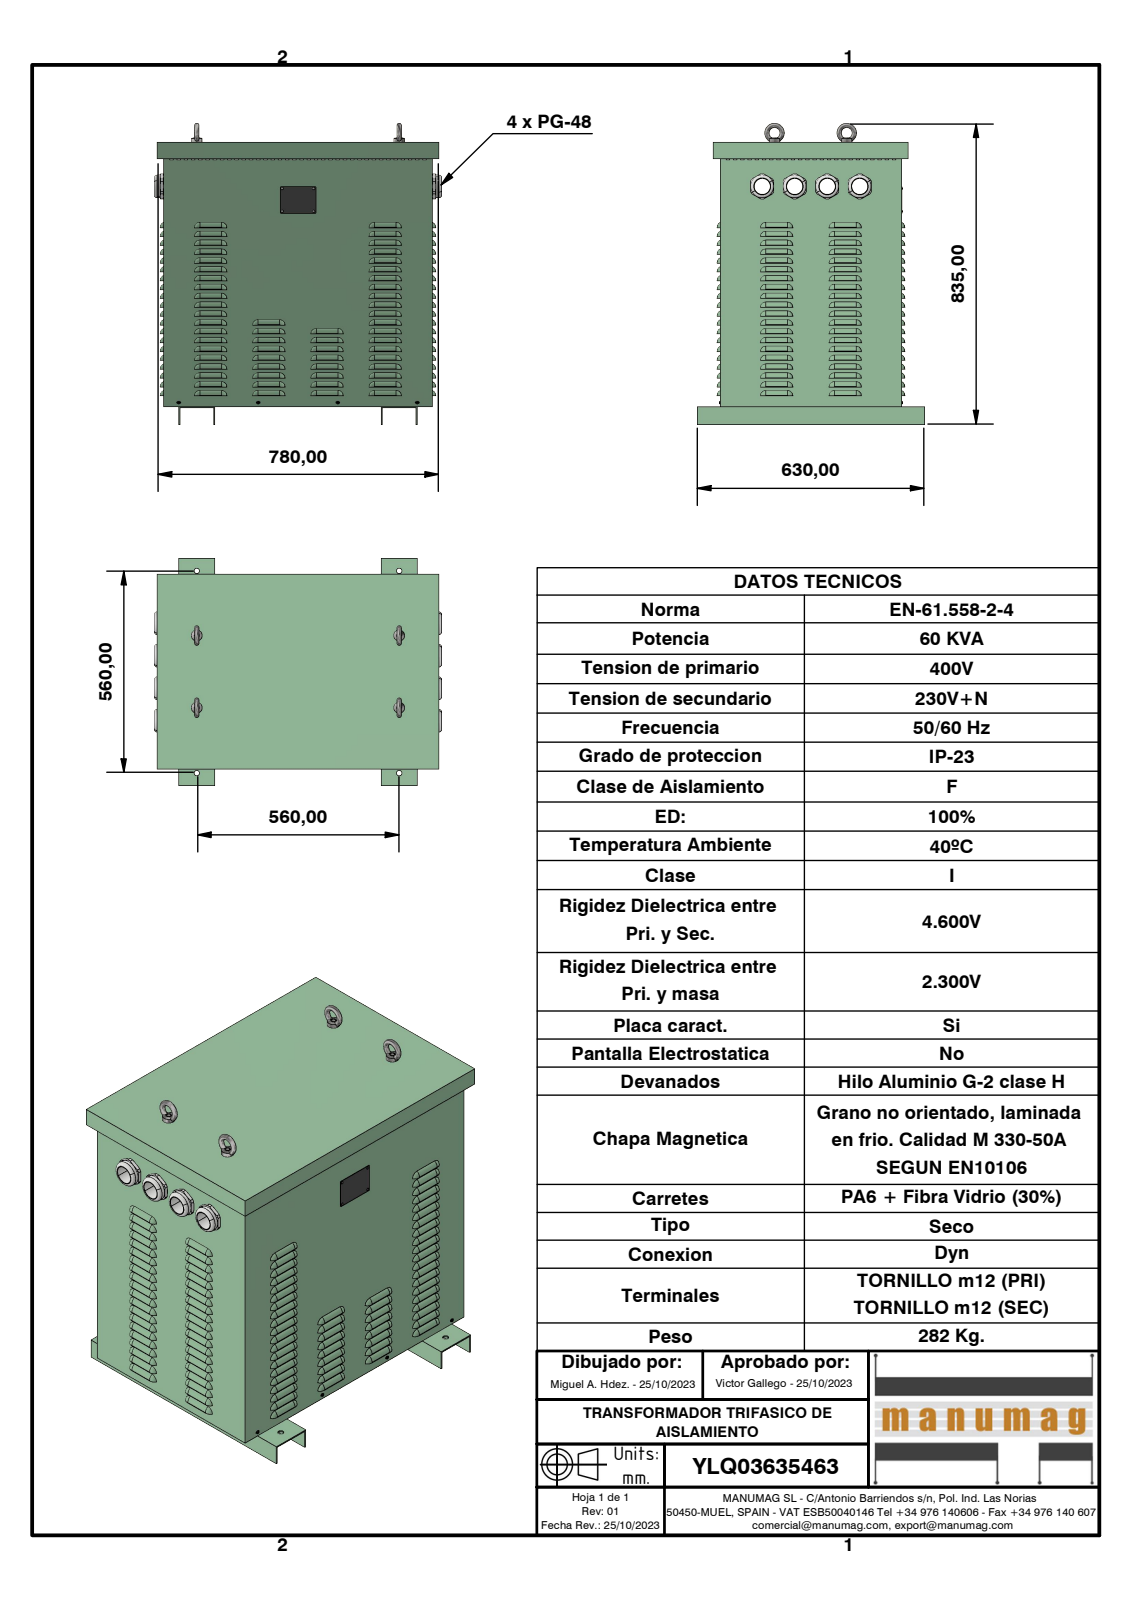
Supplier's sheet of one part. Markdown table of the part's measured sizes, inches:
| quantity | value |
| --- | --- |
| part name | YLQ03635463; JE200 CUERPO; JE160 EXPORT JE200 EXPORT NACIONAL BASE; JE160 EXPORT JE200 EXPORT NACIONAL PATA (+6 more) |
| STEP written by | Autodesk Inventor 2023 (AUTOMOTIVE_DESIGN) |
| units | inches |
| bodies | 30 solids, 4663 faces (1571 planar, 1992 cylindrical, 1100 other) |
| overall size | 32.874 × 31.31 × 24.803 |
| volume | 463 in³ |
| surface area | 9 880 in² |
| round holes (diameter × count) | 0.433 × 936, 0.591 × 12, 0.157 × 4, 0.197 × 4, 0.398 × 4, 1.732 × 4, 2.362 × 4 |
| round bosses / shafts (diameter × count) | 2.48 × 4, 2.335 × 4, 2.329 × 4, 2.269 × 4, 1.181 × 4, 0.157 × 4, 0.143 × 4, 0.126 × 4 |
| partial cylindrical surfaces (radius × count) | 0.551 × 194, 0.276 × 80, 0.591 × 80, 0.098 × 8, 0.079 × 4, 1.378 × 4 |
| main face-to-face distances | 0.079, 19.685, 28.74, 29.213, 19.606, 19.764, 28.819, 29.134, 28.661, 29.291 |
| hole center spacings | 0.591, 1.181, 1.32, 8.053, 6.288, 8.031, 5.113, 6.26 |
